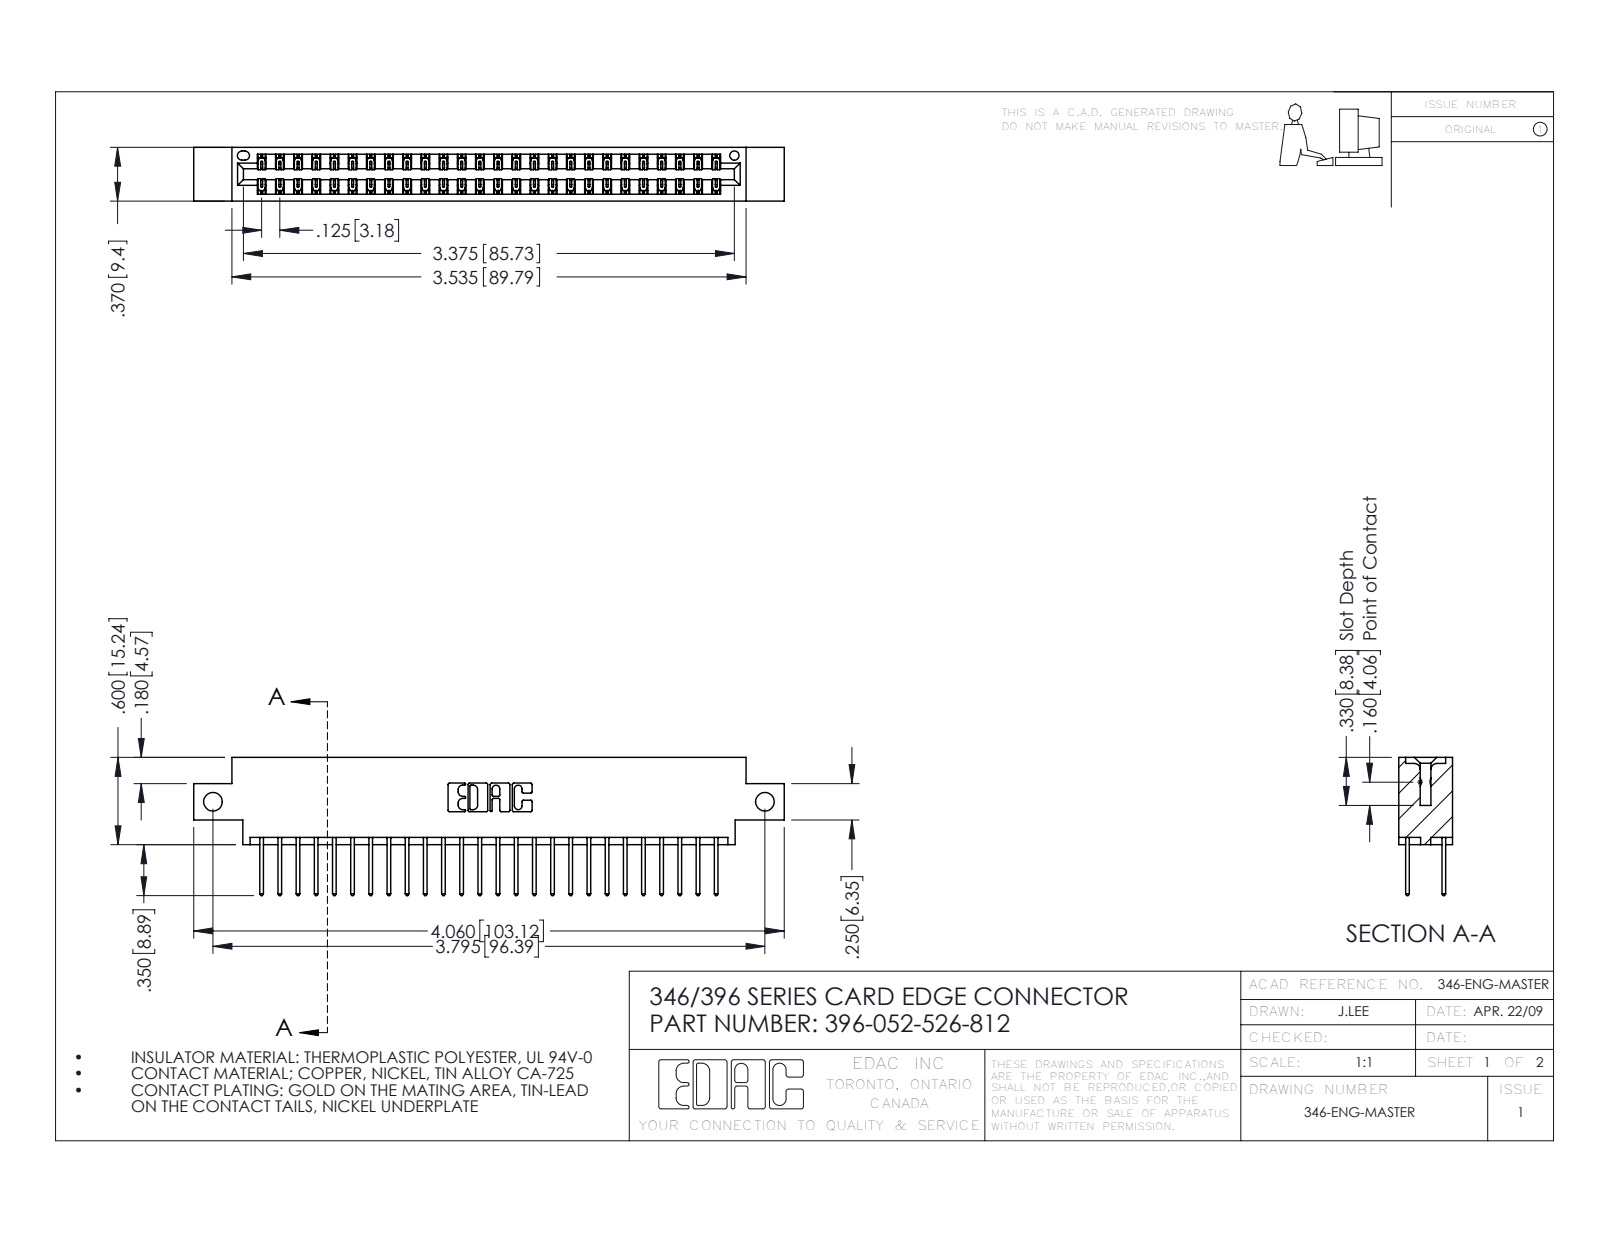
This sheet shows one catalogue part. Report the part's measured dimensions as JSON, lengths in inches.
{"part_name": "396-052-526-812; 345-292-001_345-293-126; 346 Part_0.170 Offset - Side Mount", "step_written_by": "SolidWorks 2016 (CONFIG_CONTROL_DESIGN)", "units": "inches", "bodies": {"solids": 53, "faces": 2830, "planar": 1900, "cylindrical": 930, "other": 0}, "overall_size": [4.06, 0.95, 0.37], "volume_in3": 0.597, "surface_area_in2": 21.09, "round_holes": [[0.128, 2], [0.064, 1]], "partial_cylinders_radius": [[0.006, 78], [0.01, 52], [0.01, 22], [0.007, 6], [0.031, 6], [0.026, 3], [0.014, 2], [0.022, 2]], "face_to_face_distances": [0.048, 0.322, 0.25, 0.37, 0.072, 0.298, 0.025, 0.275, 0.148, 0.222], "hole_center_spacings": [3.795]}
